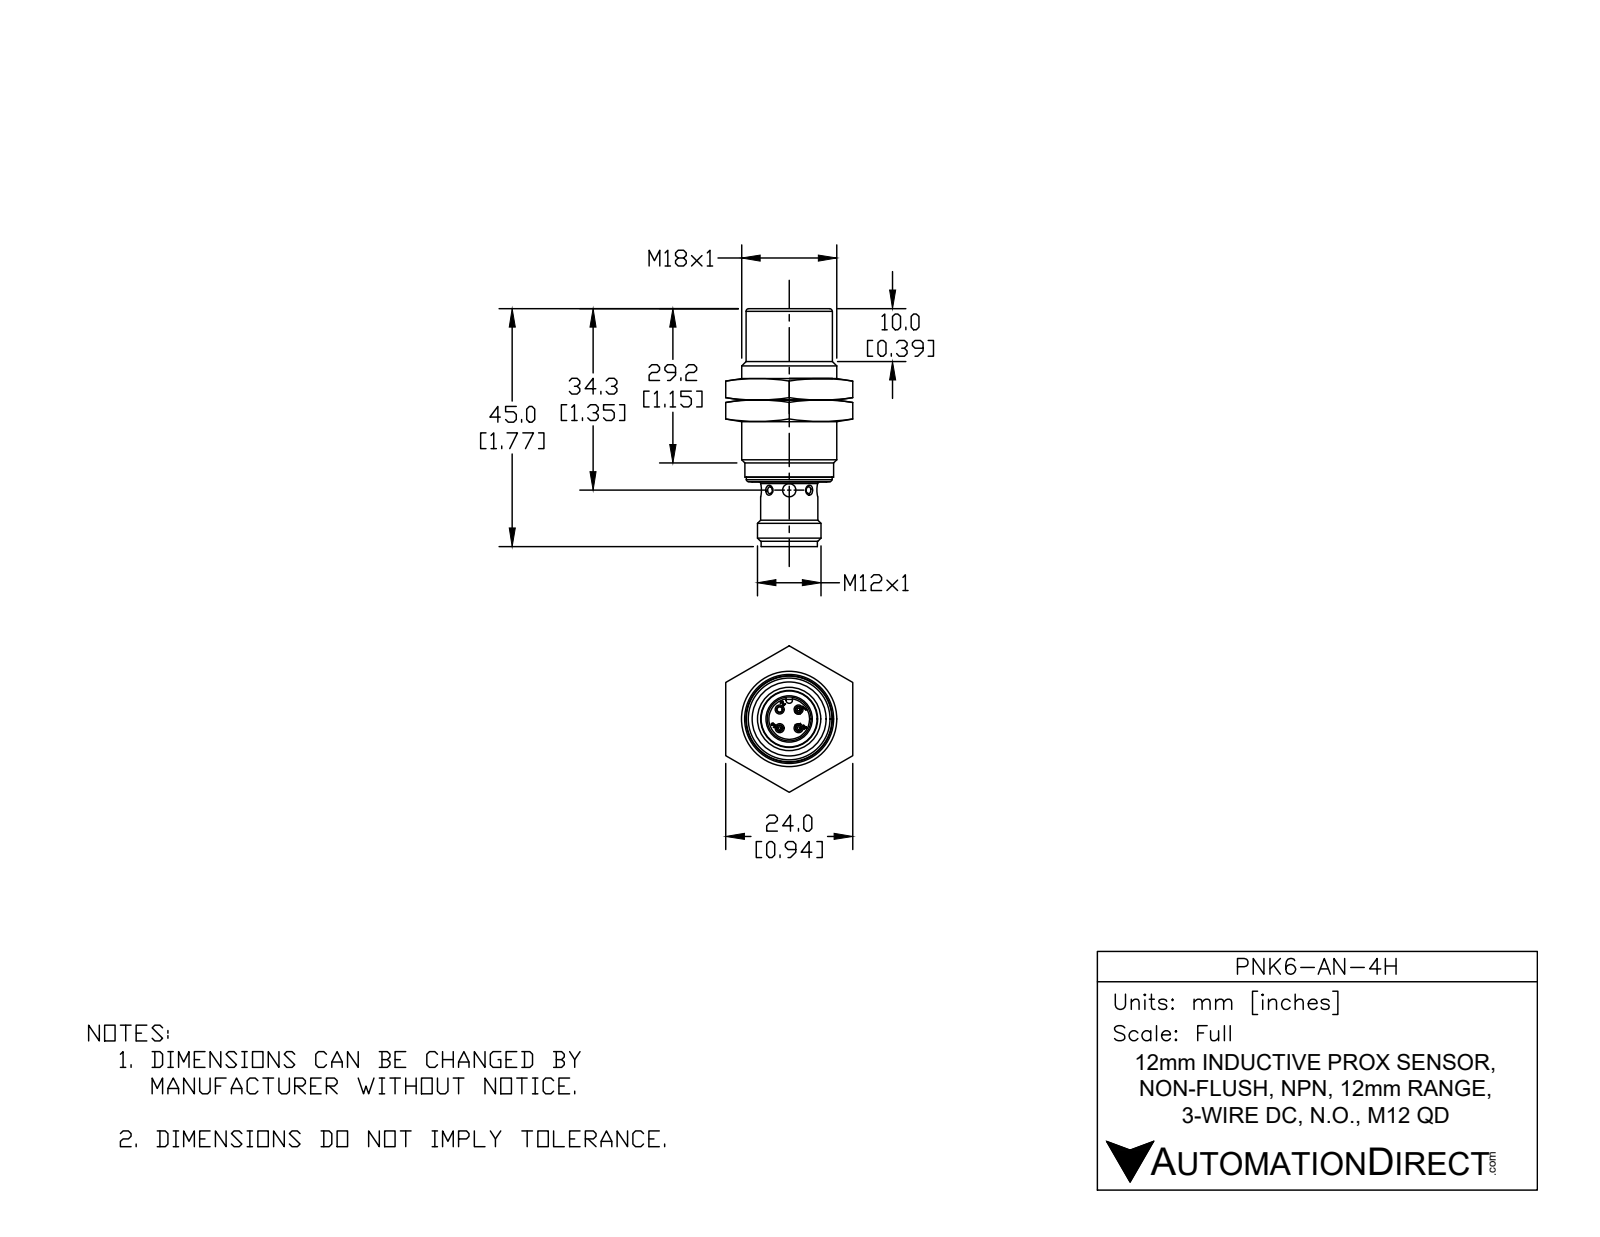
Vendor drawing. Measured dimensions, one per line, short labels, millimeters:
name: PNK6-AN-4H
written by: SolidWorks 2017 (AUTOMOTIVE_DESIGN)
unit: mm
bodies: 1 solid, 476 faces (118 planar, 129 cylindrical, 229 other)
size: 45 × 18 × 18
volume: 6 570 mm³; area: 4 930 mm²
holes: 3× ⌀1, 3× ⌀1.1, 2× ⌀2.5, 1× ⌀1, 1× ⌀8.2, 1× ⌀8.3, 1× ⌀10, 1× ⌀15.7
bosses: 9× ⌀1, 1× ⌀18, 1× ⌀16.8, 1× ⌀16.3, 1× ⌀16.2, 1× ⌀15.6, 1× ⌀12, 1× ⌀10.8
rounds: 24× R0.1, 6× R1, 6× R1.8, 1× R0.6, 1× R0.8
face distances: 11.5, 0.8, 10.7, 31.4, 30.7, 19.9, 32.8, 1.4, 32.1, 21.3
hole spacings: 2.5, 3.5, 5
